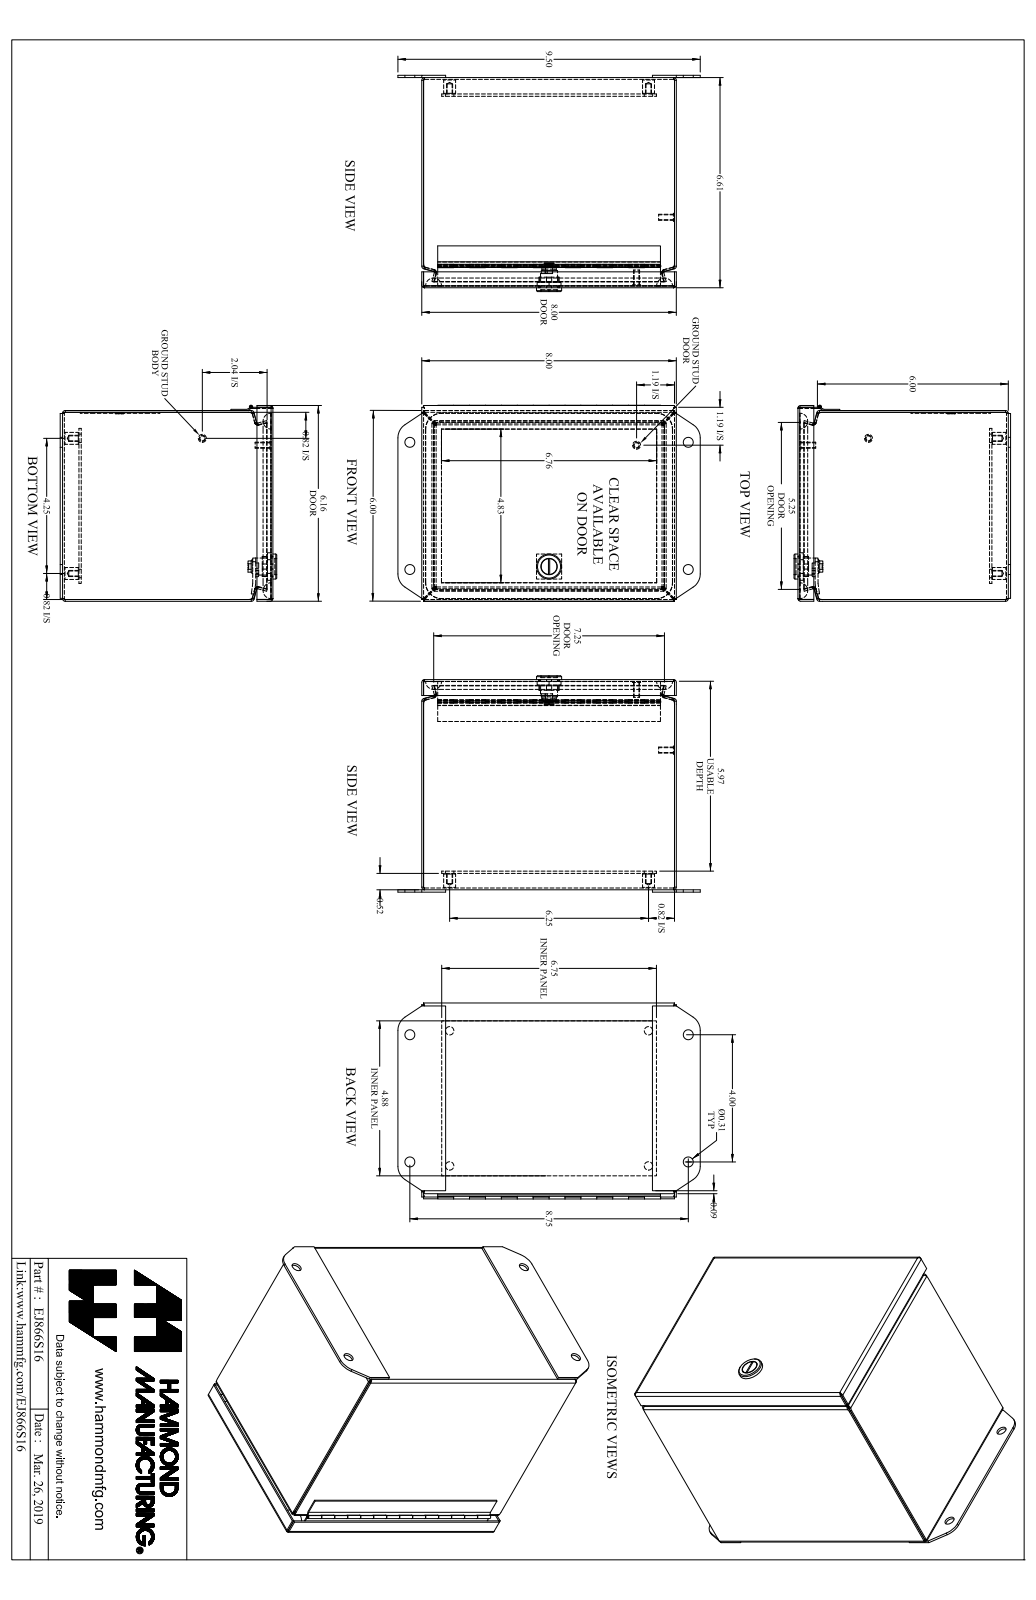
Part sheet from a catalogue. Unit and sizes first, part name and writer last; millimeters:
Units: millimetres
Overall size (bounding box): 241.3 × 172.8 × 156.6
Round holes (diameter × count): ⌀4 ×4, ⌀6.7 ×4, ⌀8 ×4, ⌀1.3 ×1, ⌀13.1 ×1
Round bosses / shafts (diameter × count): ⌀9.5 ×4, ⌀6.4 ×2, ⌀4.8 ×2, ⌀20 ×1, ⌀13.6 ×1, ⌀12.6 ×1, ⌀11 ×1, ⌀2.5 ×1
Partial cylindrical surfaces — rounded edges, fillets, slot ends (radius × count): R0.7 ×16, R2.2 ×16, R7.1 ×12, R6.4 ×4, R12.7 ×4, R12.7 ×4, R1.5 ×2, R0.8 ×1
Main face-to-face distances: 1.4, 166.5, 151, 201.8, 1.8, 15, 149.5, 167.9, 152.4, 165
Hole centre spacings: 31.9, 109.5, 190.6, 217.4, 79.6, 101.6, 108, 111.2
Volume: 381 500 mm³ · Surface area: 499 900 mm²
Bodies: 16 solids, 564 faces (294 planar, 190 cylindrical, 80 other)
Part name (STEP PRODUCT): EJ866S16_Default
STEP written by: SolidWorks 2019 (CONFIG_CONTROL_DESIGN)
